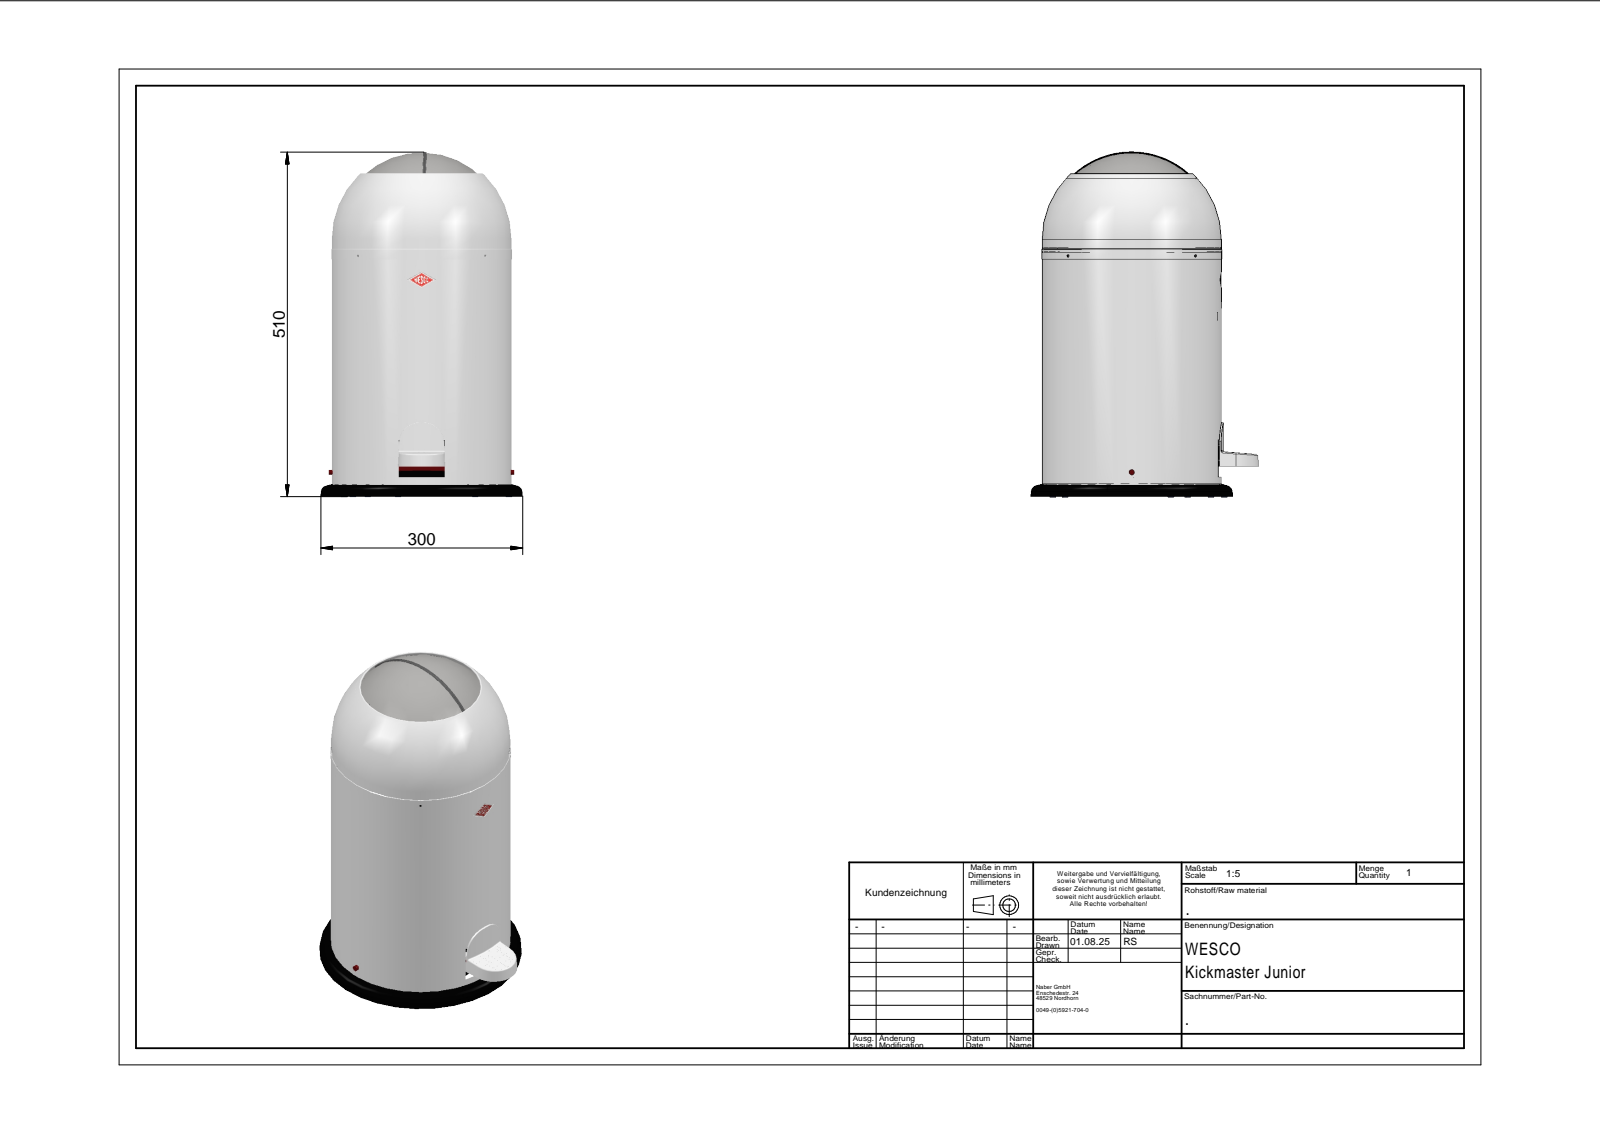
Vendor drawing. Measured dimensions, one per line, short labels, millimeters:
name: 180 212 Singel Master|18021201 Rumpf mit Tretbügel:1#18021201|18021201-01 Rumpf:1#18021201-01 Rumpf;Volumenkörper2
written by: Spatial InterOp 3D (AUTOMOTIVE_DESIGN)
unit: mm
bodies: 83 solids, 3200 faces (1476 planar, 693 cylindrical, 1031 other)
size: 511.54 × 337.93 × 300
volume: 1 307 000 mm³; area: 1 847 000 mm²
holes: 10× ⌀5.1, 9× ⌀3.5, 8× ⌀4, 2× ⌀2.25, 2× ⌀10, 1× ⌀4.5, 1× ⌀6.4, 1× ⌀8.1, 1× ⌀177.75, 1× ⌀250, 1× ⌀253, 1× ⌀257
bosses: 10× ⌀9, 10× ⌀5, 2× ⌀6, 2× ⌀4, 1× ⌀270, 1× ⌀267.3, 1× ⌀266, 1× ⌀258.4
rounds: 108× R0.2, 89× R0.75, 79× R0.5, 21× R1, 21× R1.5, 12× R3, 11× R2, 8× R2.5
face distances: 2, 364.25, 366.25, 362.25, 325.5, 38.75, 1.5, 4, 327.5, 3
hole spacings: 141.5, 245.08, 181.91, 96.79, 278.7, 278.69, 141.49, 181.9
